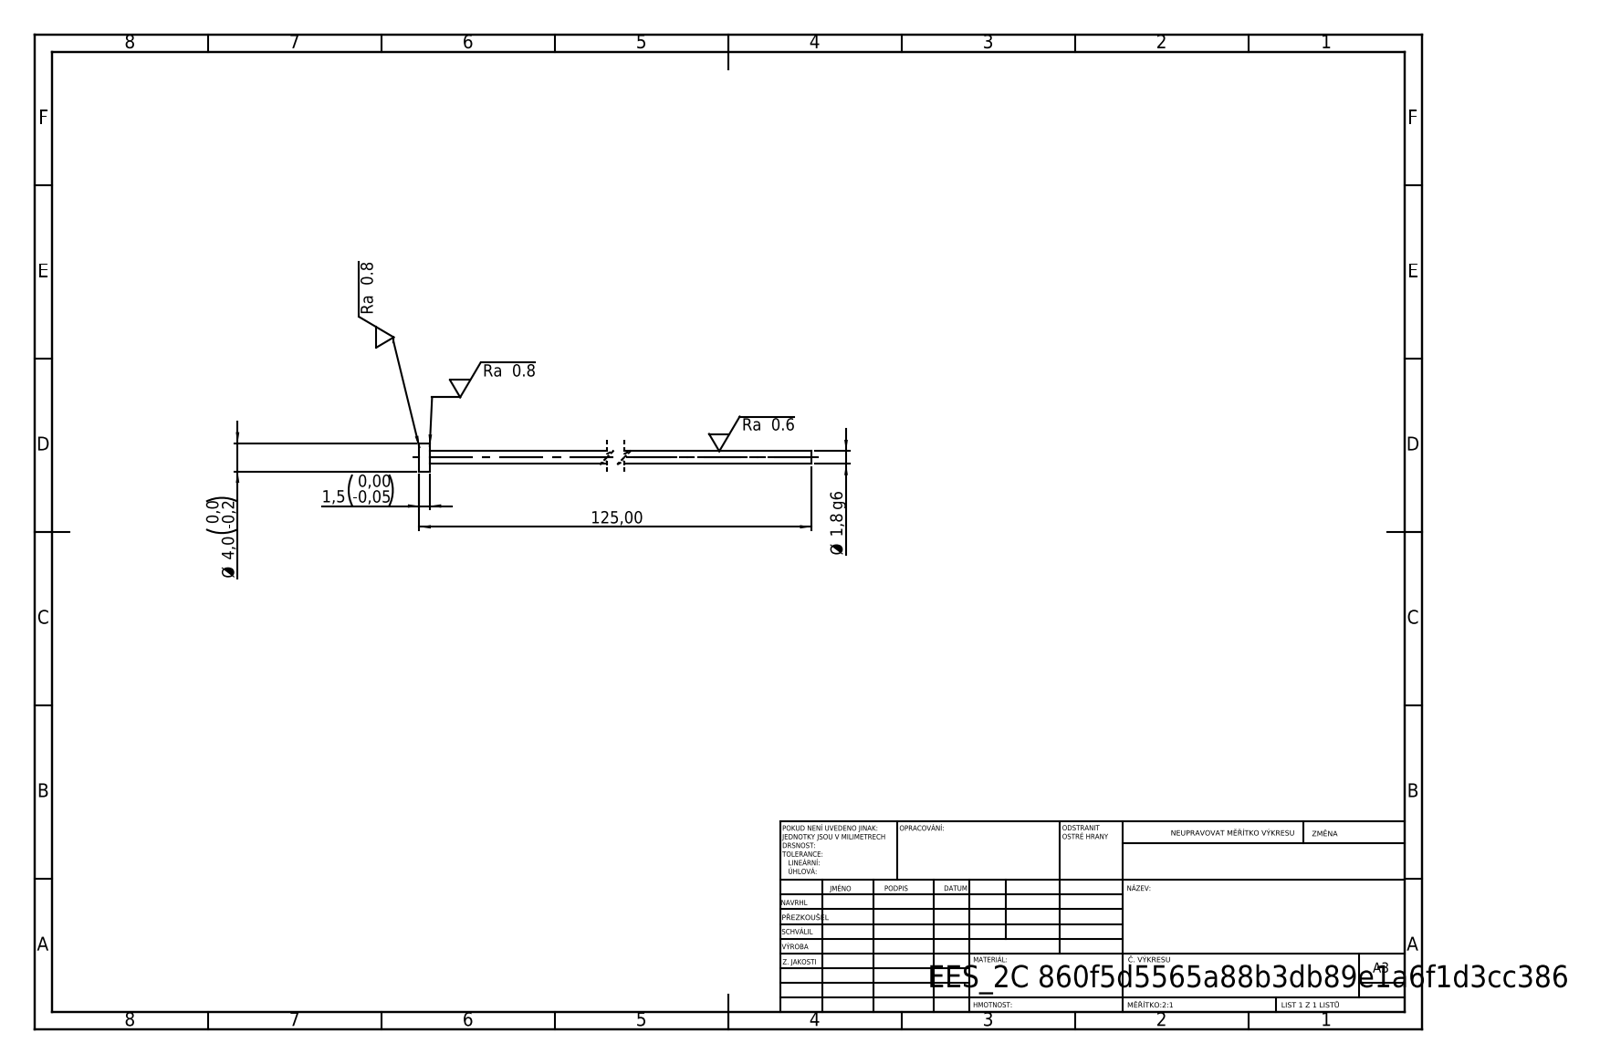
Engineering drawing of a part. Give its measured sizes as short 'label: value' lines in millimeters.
written by: SolidWorks 2019 (CONFIG_CONTROL_DESIGN)
unit: mm
bodies: 1 solid, 7 faces (3 planar, 4 cylindrical, 0 other)
size: 125 × 4 × 4
volume: 333 mm³; area: 742 mm²
bosses: 1× ⌀4, 1× ⌀1.8
face distances: 1.5, 125, 123.5
